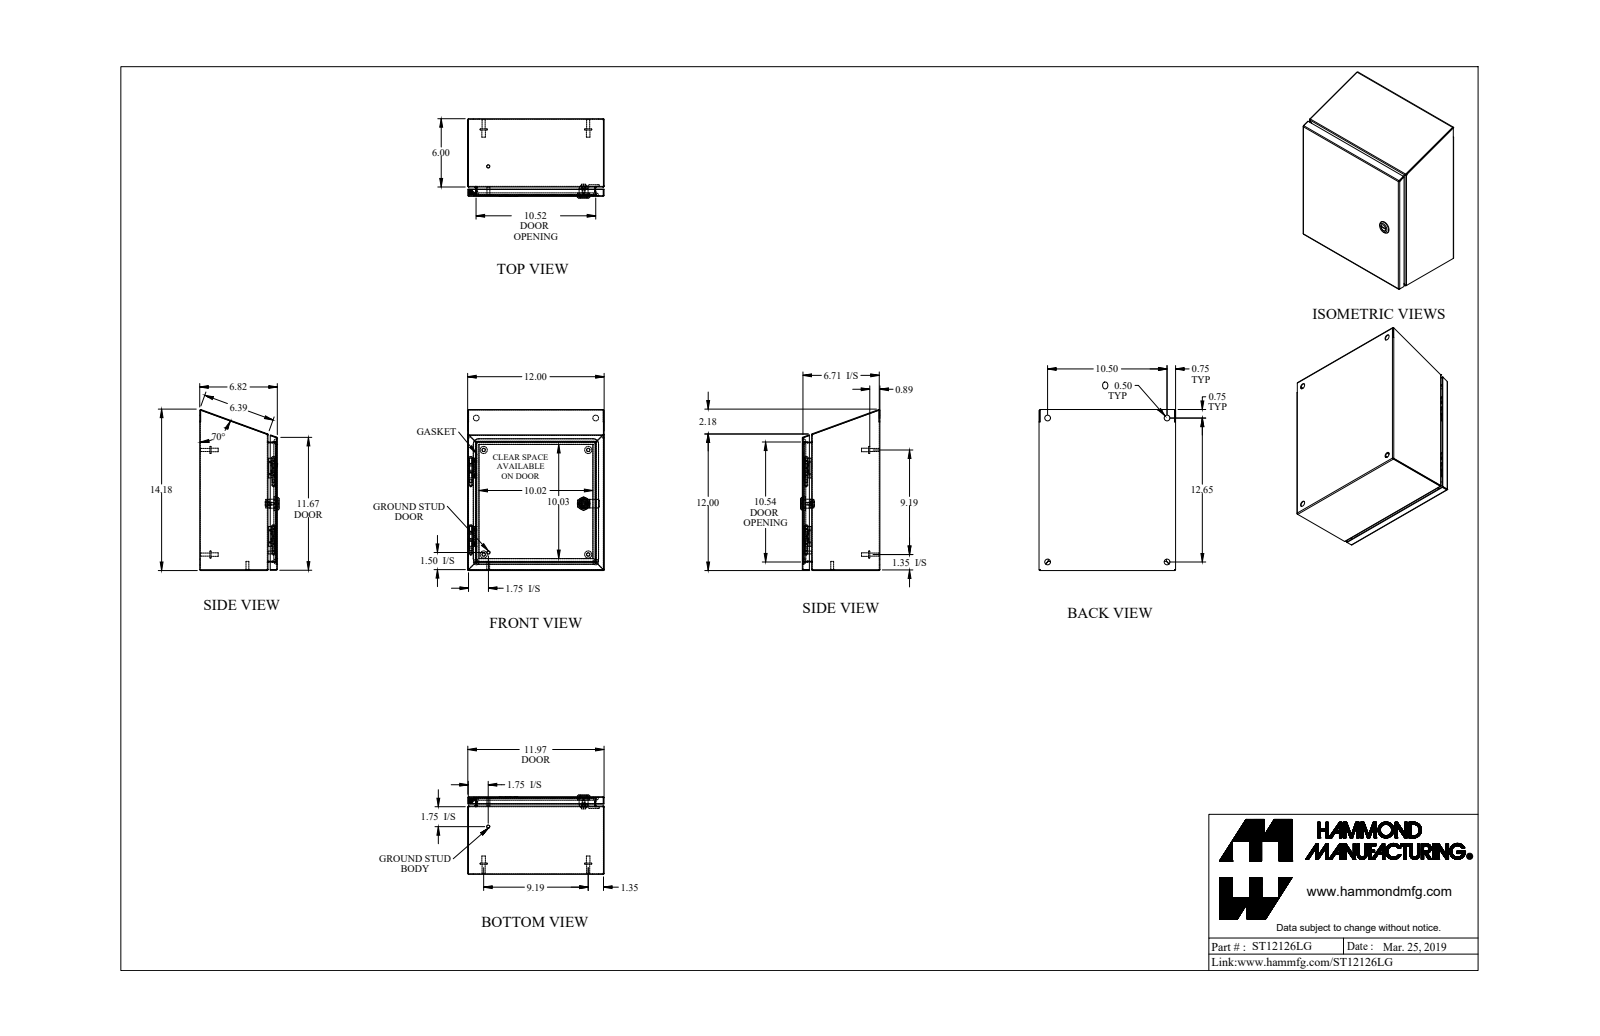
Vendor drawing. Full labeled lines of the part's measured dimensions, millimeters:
Part name (STEP PRODUCT): ST12126LG
STEP written by: SolidWorks 2018 (AUTOMOTIVE_DESIGN)
Units: millimetres
Bodies: 21 solids, 632 faces (303 planar, 197 cylindrical, 132 other)
Overall size (bounding box): 359.3 × 304.8 × 177.3
Volume: 744 800 mm³ · Surface area: 985 800 mm²
Round holes (diameter × count): ⌀12.7 ×4, ⌀4.4 ×1, ⌀5.9 ×1, ⌀6.1 ×1, ⌀6.1 ×1, ⌀15.9 ×1, ⌀19.9 ×1
Round bosses / shafts (diameter × count): ⌀15.9 ×4, ⌀8 ×4, ⌀6.9 ×4, ⌀7.1 ×2, ⌀6.4 ×2, ⌀27.9 ×1, ⌀13.3 ×1, ⌀11.6 ×1
Partial cylindrical surfaces — rounded edges, fillets, slot ends (radius × count): R0.7 ×21, R2.2 ×21, R6.4 ×11, R0.2 ×4, R1.6 ×4, R12.7 ×4, R3.2 ×2, R0.5 ×1
Main face-to-face distances: 1.4, 171.8, 170.4, 303.4, 173.3, 301.9, 304.8, 1.4, 151, 20.9
Hole centre spacings: 266.7, 321.2, 417.5, 133, 192.9, 272.9, 306.6
